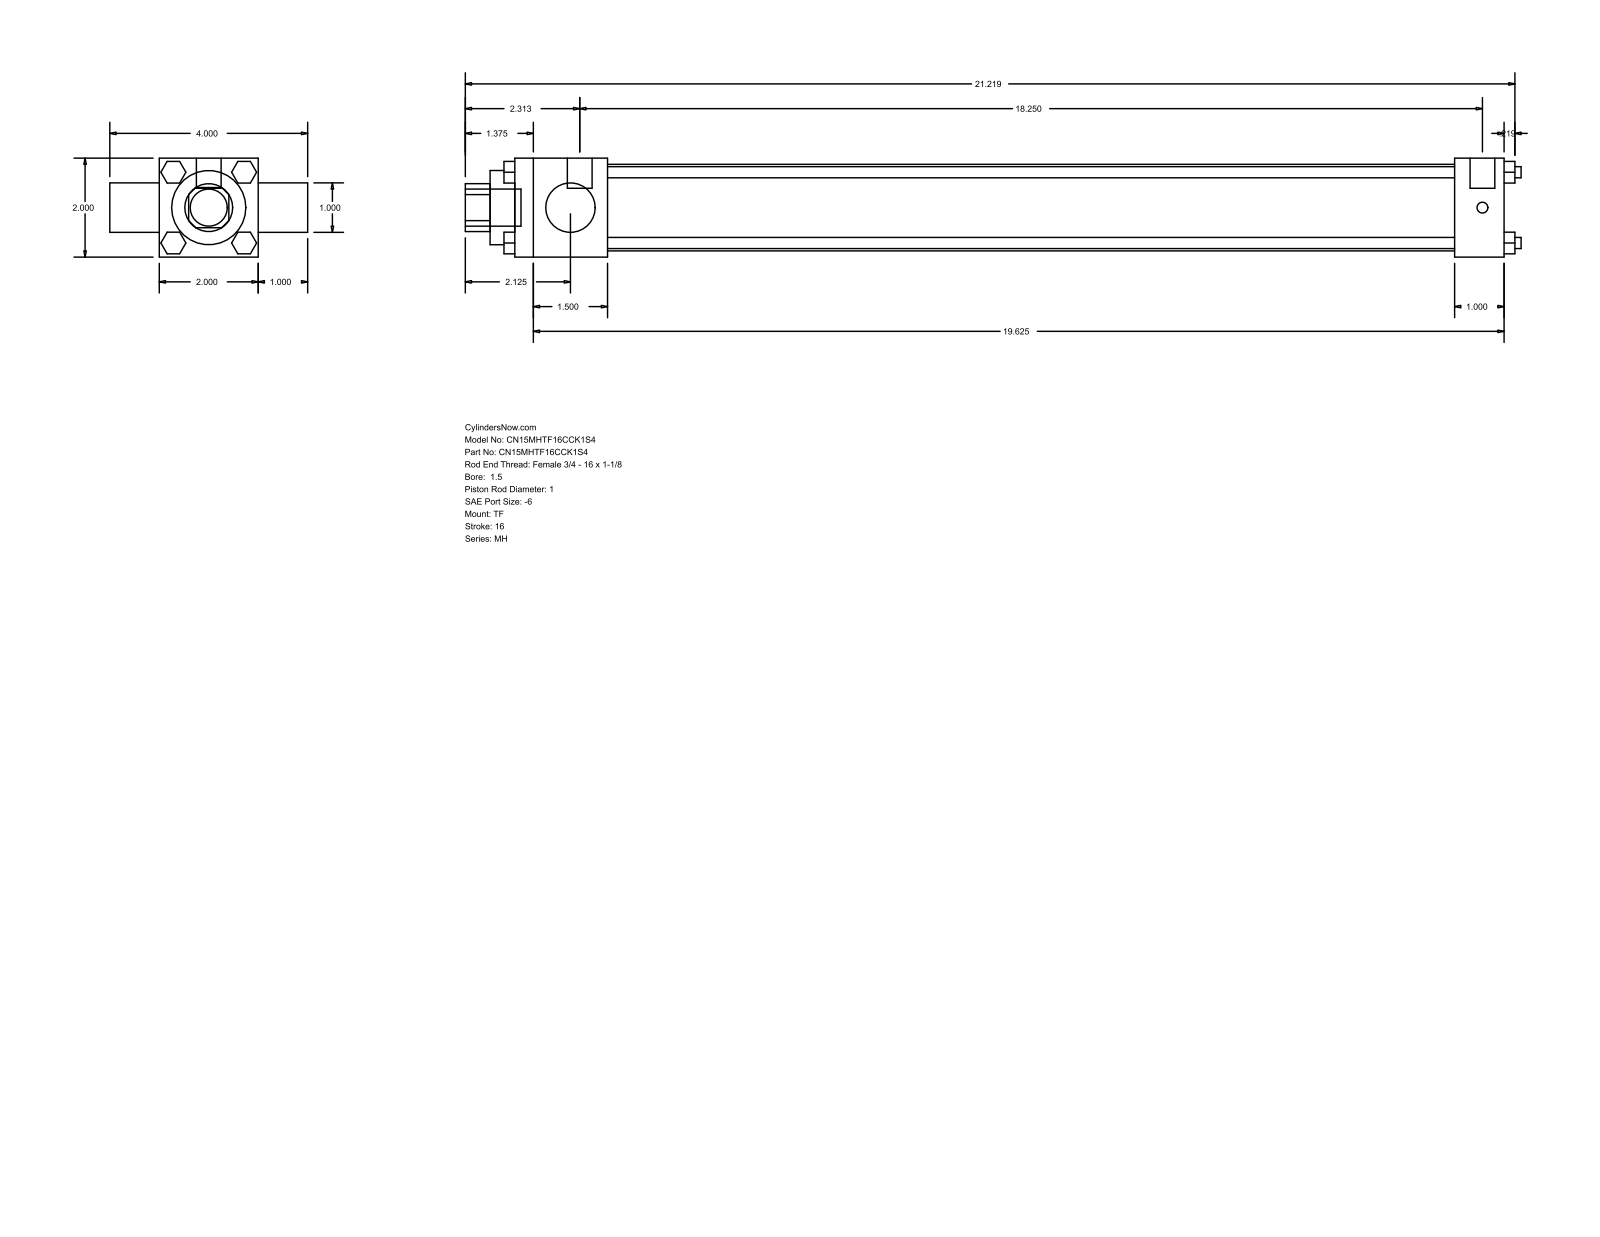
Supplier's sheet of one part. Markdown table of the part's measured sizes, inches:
| quantity | value |
| --- | --- |
| part name | MH_TF__0150_1 |
| STEP written by | GSSL Pune (CONFIG_CONTROL_DESIGN) |
| units | inches |
| bodies | 0 solids, 120 faces (92 planar, 28 cylindrical, 0 other) |
| overall size | 21.344 × 4 × 2 |
| round holes (diameter × count) | 1 × 2, 1.5 × 1, 1.75 × 1 |
| round bosses / shafts (diameter × count) | 0.225 × 4, 0.219 × 3, 0.5 × 2, 0.75 × 1 |
| partial cylindrical surfaces (radius × count) | 0.484 × 1 |
| main face-to-face distances | 2, 1, 20, 3, 1.875, 18.125, 19, 17.125, 20.219, 0.5 |
